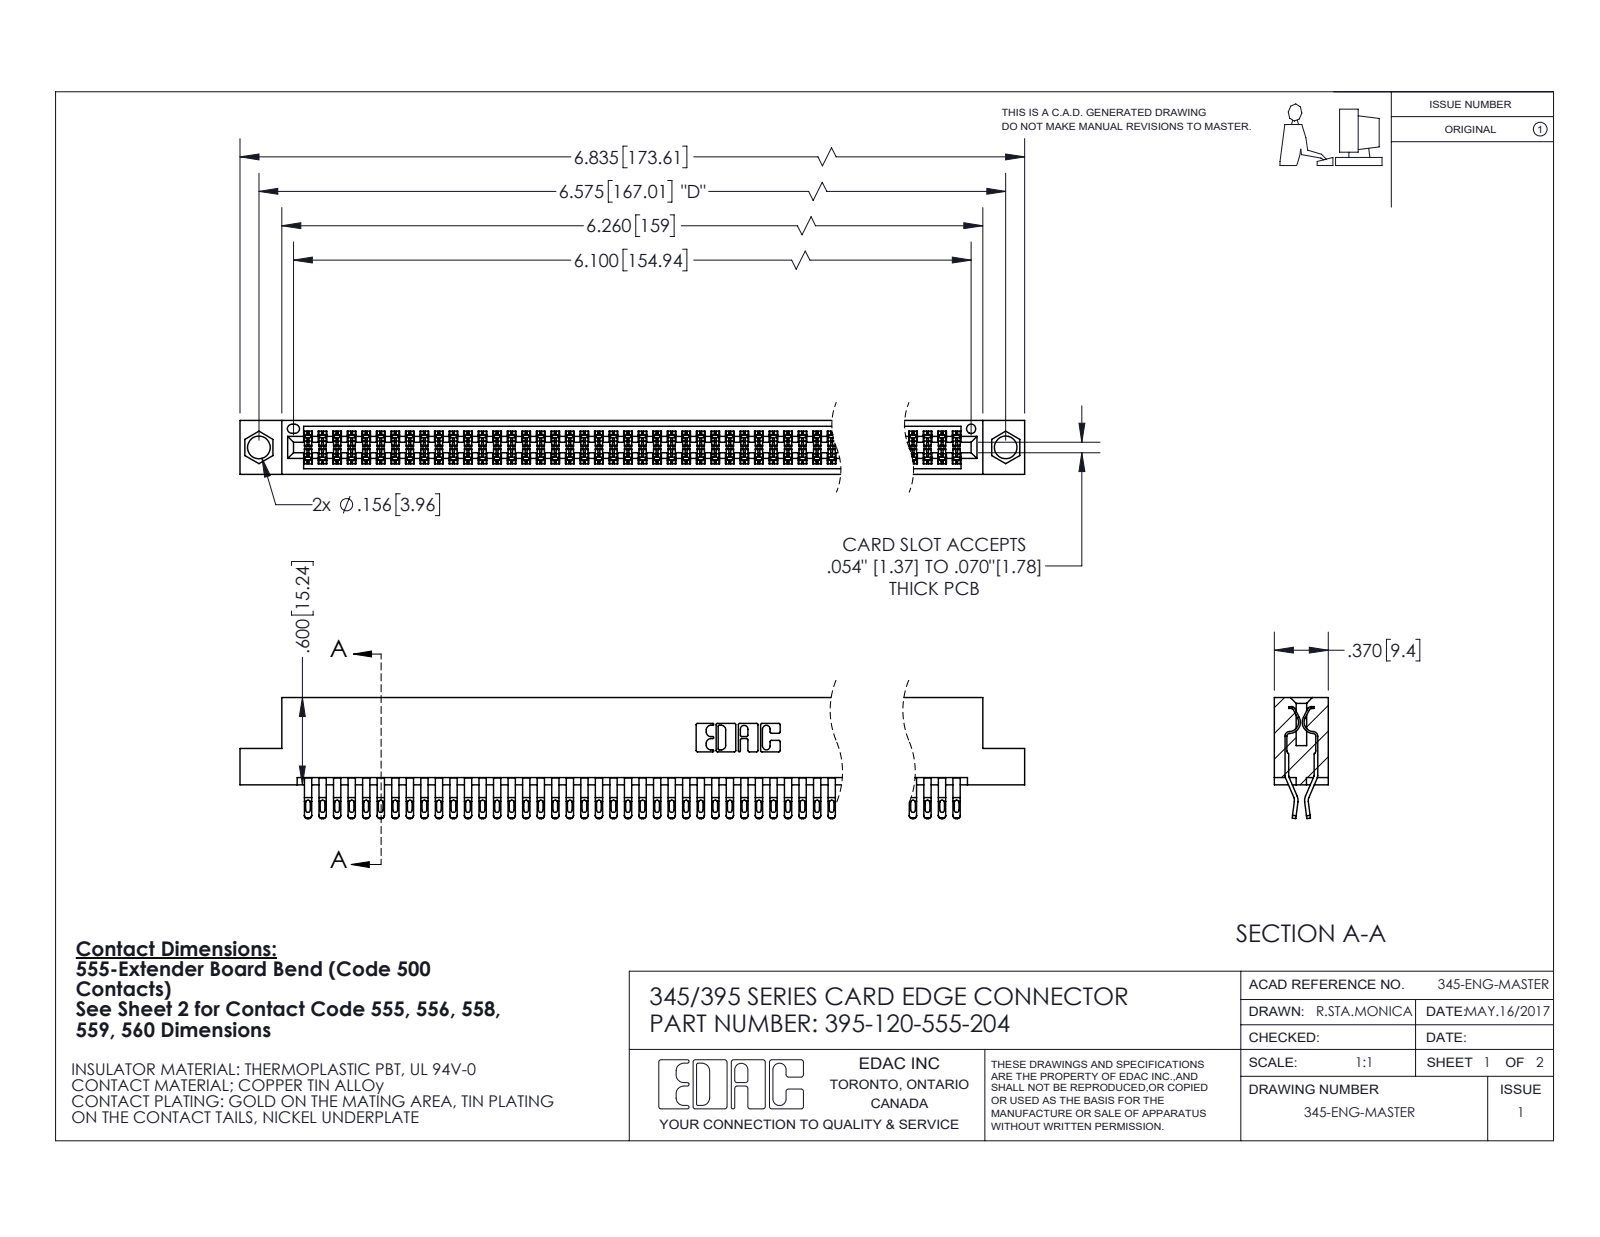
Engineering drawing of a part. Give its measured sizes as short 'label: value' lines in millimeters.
name: 345 Part_Flush Mounting Lugs - 0.156 Dia-TI; 345-292-001_555 Tail; 395-120-555-204
written by: SolidWorks 2020 (CONFIG_CONTROL_DESIGN)
unit: mm
bodies: 121 solids, 6860 faces (3814 planar, 3046 cylindrical, 0 other)
size: 173.6 × 21.1 × 9.4
volume: 17 270 mm³; area: 26 940 mm²
holes: 2× ⌀4, 1× ⌀1.6
rounds: 300× R0.4, 240× R0.2, 240× R0.5, 22× R0.3, 6× R0.2, 6× R0.8, 3× R0.7, 2× R0.3
face distances: 7.6, 1.8, 0.6, 9.4, 5.1, 2.5, 6.9, 5.7, 4.4, 3.8
hole spacings: 6.9, 161, 167
